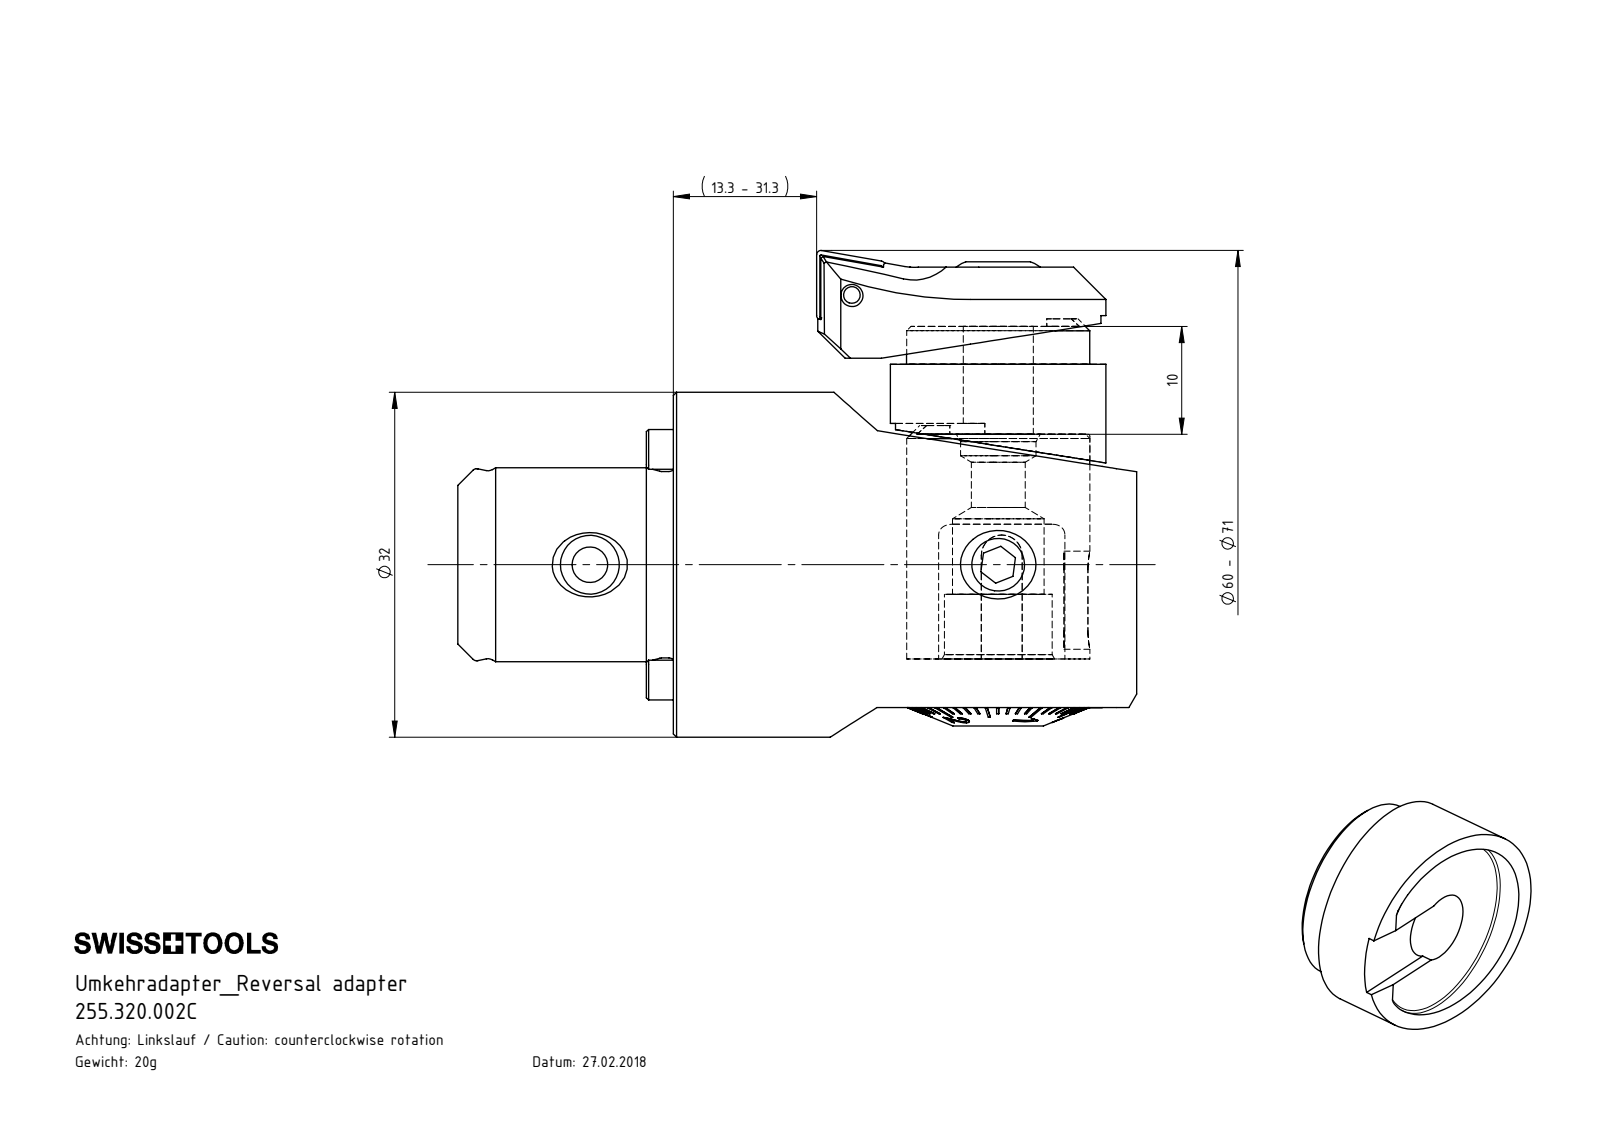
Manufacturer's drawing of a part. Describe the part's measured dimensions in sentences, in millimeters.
The part is named "F32-U00.001.010_B; 255.320.002C". Its 3-D file was written by "SolidWorks 2017 (CONFIG_CONTROL_DESIGN)". It is 1 solid with 27 faces: 11 planar, 11 cylindrical and 5 other. Overall it measures 20 by 20 by 13.37 millimeters. Its volume is 2 568 cubic millimeters and its surface area 1 488 square millimeters. Round holes: 1 of diameter 6.5, 1 of diameter 17. Round bosses or shafts: 1 of diameter 20. Partial cylindrical surfaces (rounded edges, fillets, slot ends): 2 of radius 0.5. The main face-to-face distances are 10, 6.5, 3.5, 1, 5.5, 9, 10.7, 9.7, 4.2, 0.7.
